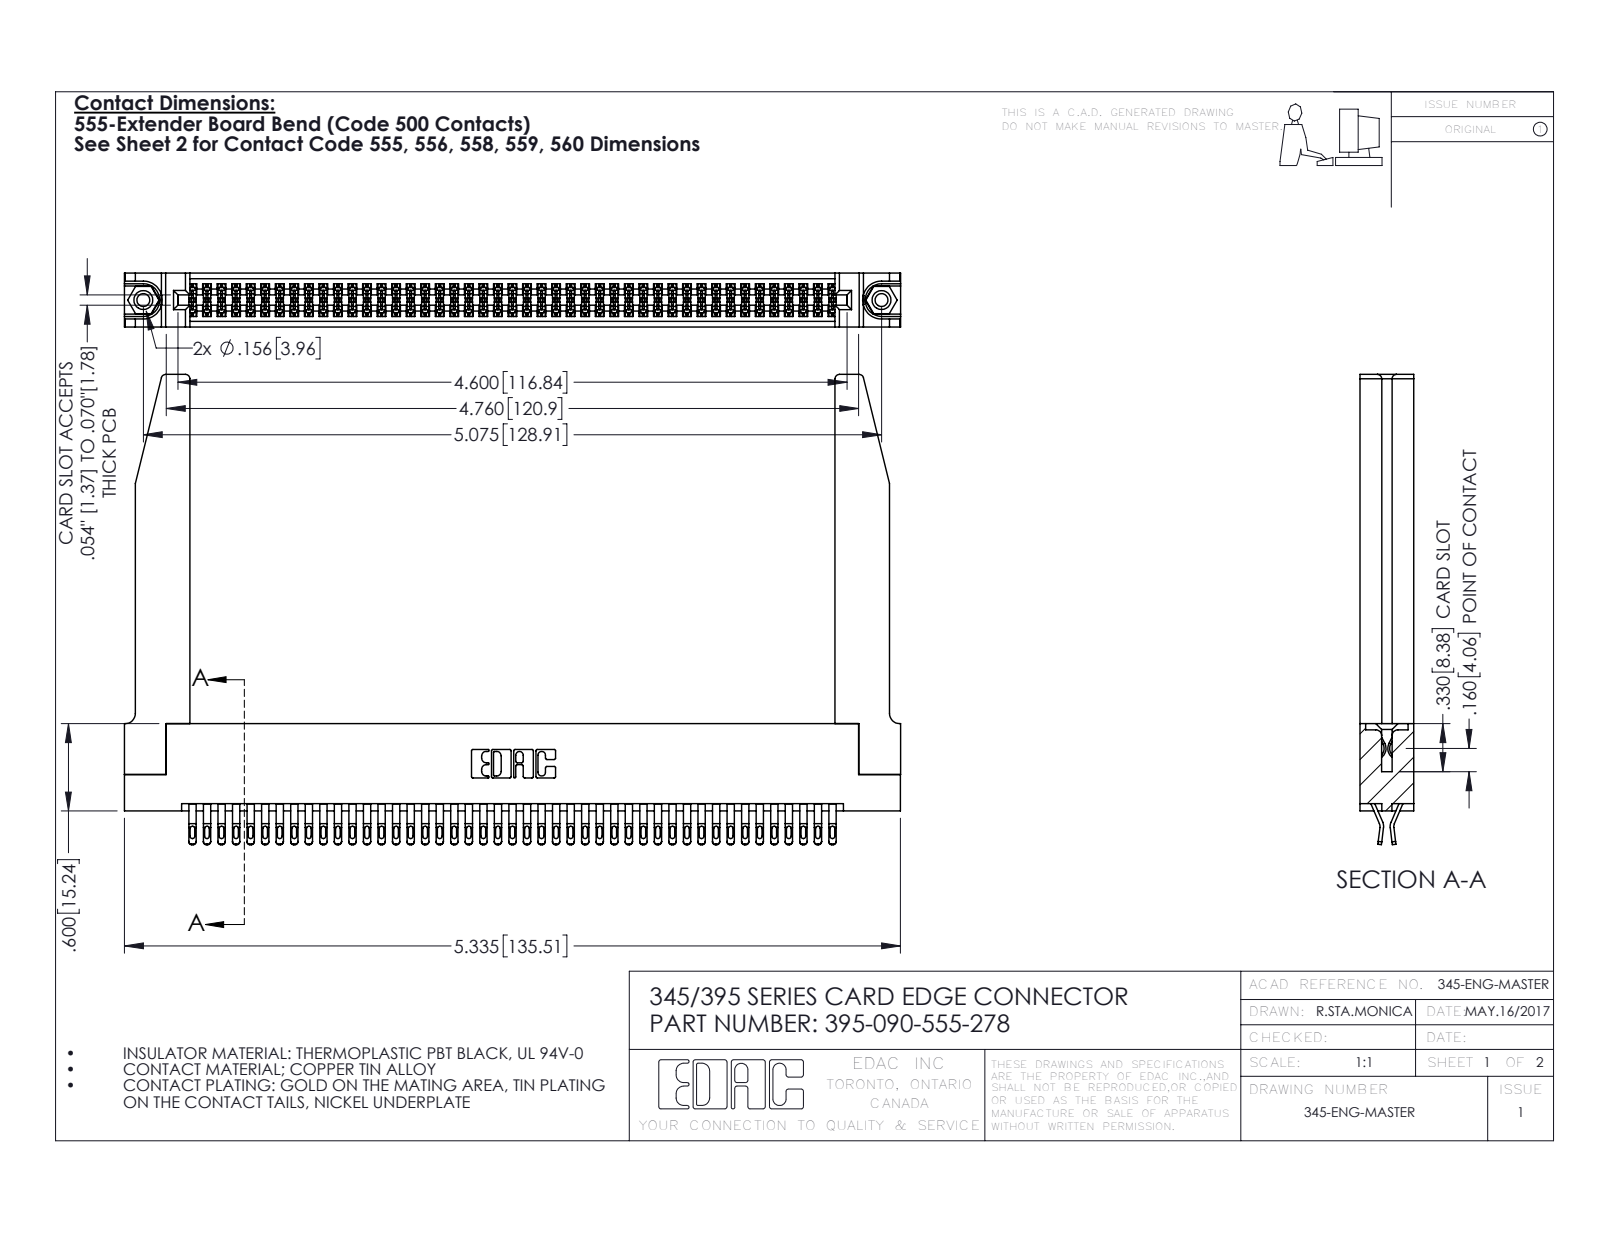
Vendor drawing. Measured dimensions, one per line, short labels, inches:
name: 345-292-001_555 Tail; 345 Part_Flush Mounting Lugs - 0.156 Dia-TH; 345-250-001_345-250-001-102; 395-090-555-278 (+1 more)
written by: SolidWorks 2016 (CONFIG_CONTROL_DESIGN)
unit: in
bodies: 95 solids, 5400 faces (3012 planar, 2336 cylindrical, 52 other)
size: 5.336 × 3.232 × 0.37
volume: 1.295 in³; area: 42.92 in²
holes: 2× ⌀0.089, 2× ⌀0.125, 2× ⌀0.156, 1× ⌀0.064
bosses: 2× ⌀0.155
rounds: 225× R0.016, 180× R0.02, 135× R0.006, 22× R0.01, 8× R0.03, 6× R0.007, 6× R0.031, 3× R0.026
face distances: 0.37, 0.072, 0.298, 0.025, 0.2, 0.098, 0.272, 0.225, 0.148, 0.15
hole spacings: 0.27, 4.839, 5.075
